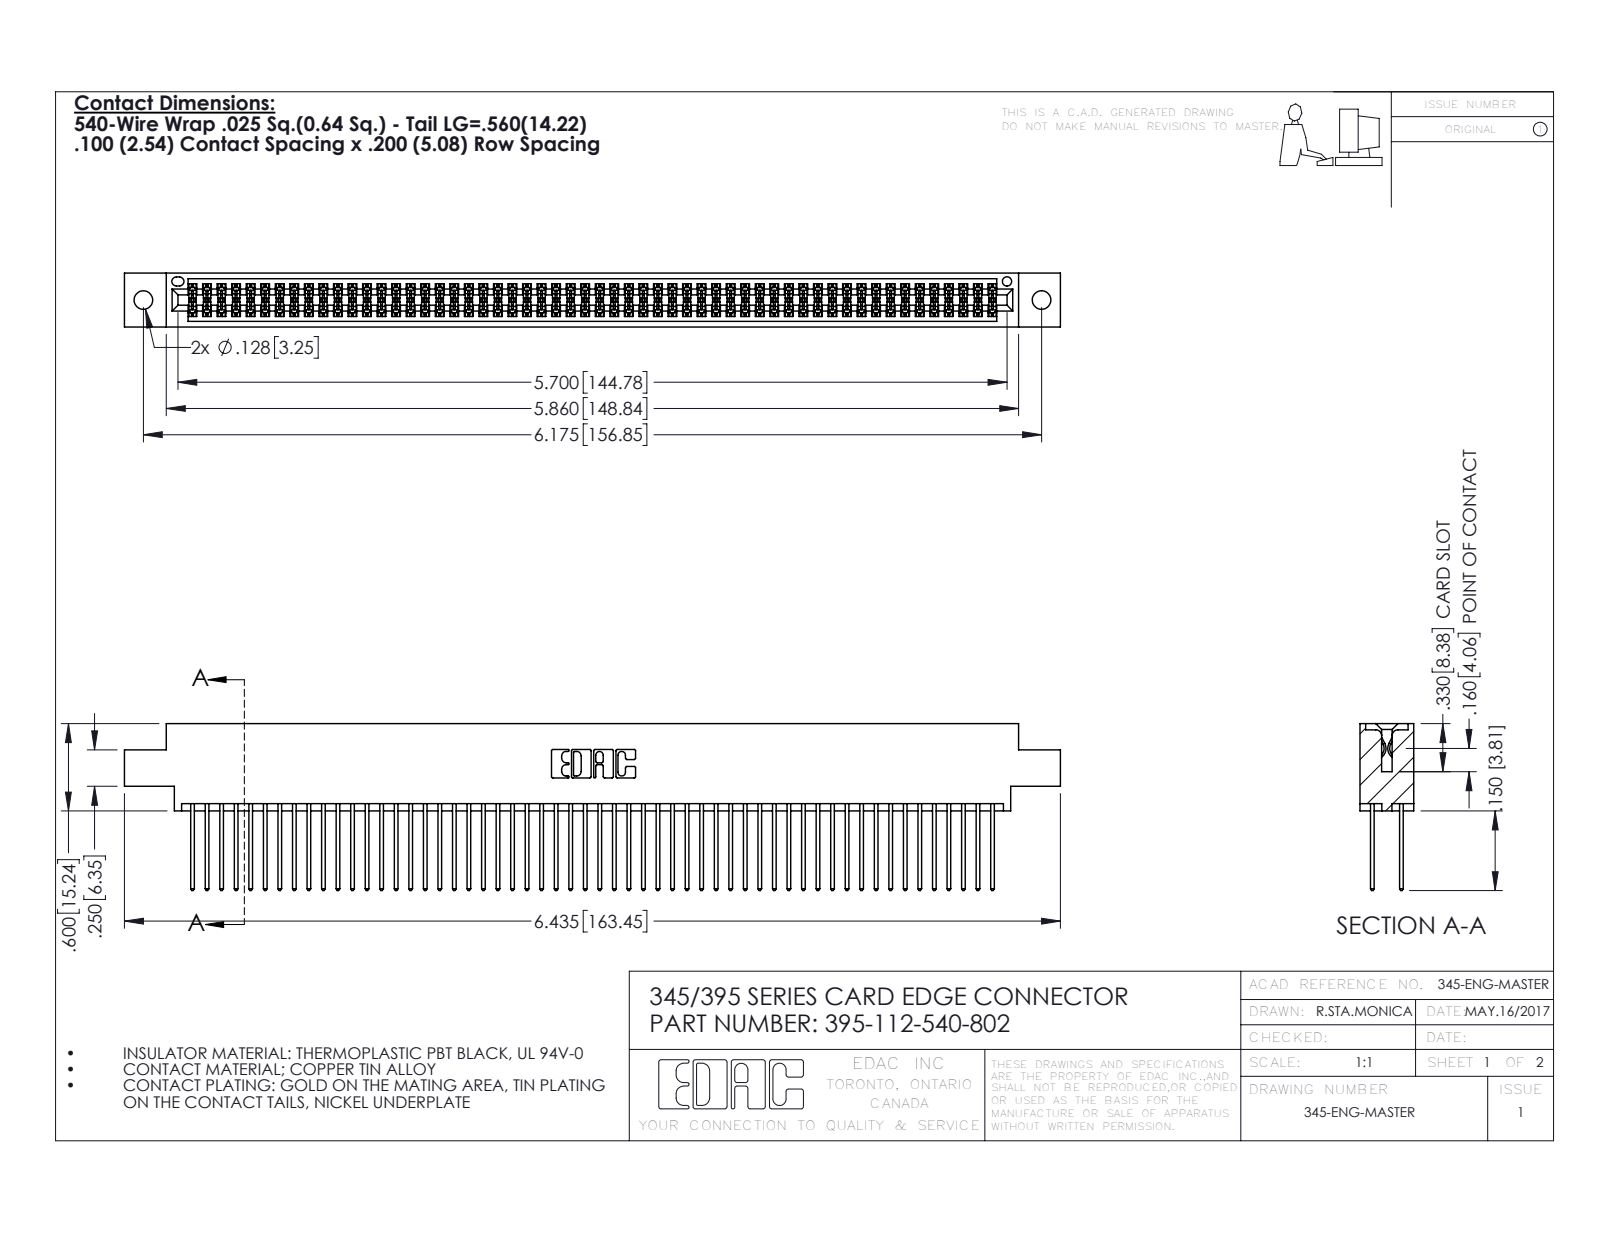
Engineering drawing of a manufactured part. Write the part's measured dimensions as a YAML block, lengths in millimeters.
part_name: "345-292-001_345-293-140; 345 Part_0.170 Offset - 0.128 Dia; 395-112-540-802"
step_written_by: "SolidWorks 2016 (CONFIG_CONTROL_DESIGN)"
units: millimeters
bodies: {solids: 113, faces: 5730, planar: 3780, cylindrical: 1950, other: 0}
overall_size: [163.4, 29.1, 9.4]
volume: 16300
surface_area: 26180
round_holes:
  - {diameter: 3.3, count: 2}
  - {diameter: 1.6, count: 1}
partial_cylinders:
  - {radius: 0.2, count: 168}
  - {radius: 0.3, count: 112}
  - {radius: 0.3, count: 22}
  - {radius: 0.2, count: 6}
  - {radius: 0.8, count: 6}
  - {radius: 0.7, count: 3}
  - {radius: 0.4, count: 2}
  - {radius: 0.5, count: 2}
face_to_face_distances: [7.6, 1.8, 5.1, 2.5, 6.9, 0.6, 9.4, 5.7, 4.4, 3.8]
hole_center_spacings: [6.9, 150.9, 156.8]
